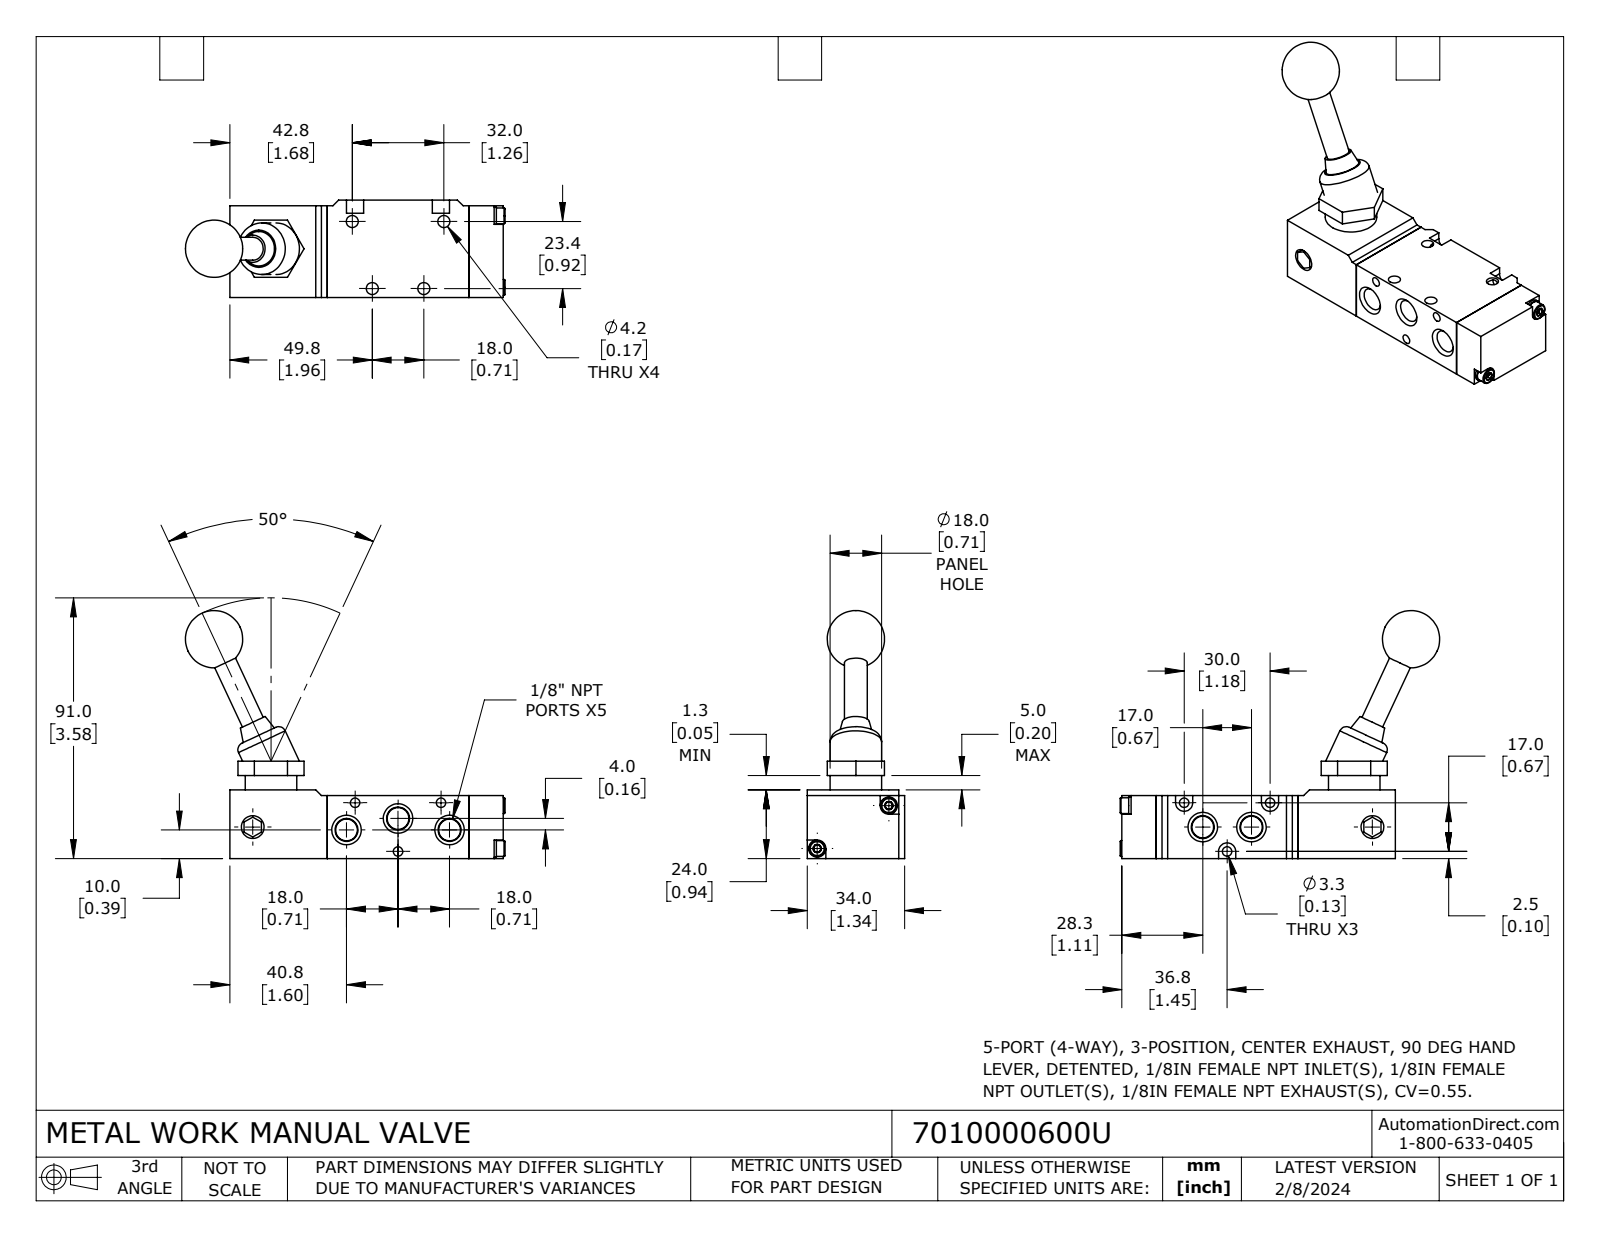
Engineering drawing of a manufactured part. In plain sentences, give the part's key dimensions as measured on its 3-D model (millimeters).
The part is named "7010000600U". Its 3-D file was written by "SolidWorks 2023 (CONFIG_CONTROL_DESIGN)". It is 8 solids with 208 faces: 105 planar, 49 cylindrical and 54 other. Overall it measures 111.6 by 86.6 by 34 millimeters. Its volume is 79 120 cubic millimeters and its surface area 22 500 square millimeters. Round holes: 4 of diameter 4.2, 3 of diameter 3.3, 2 of diameter 3, 1 of diameter 8. Round bosses or shafts: 2 of diameter 18, 2 of diameter 6, 2 of diameter 5.5, 1 of diameter 8. Partial cylindrical surfaces (rounded edges, fillets, slot ends): 3 of radius 3. The main face-to-face distances are 22, 34, 49.5, 2, 32, 12, 83.5, 24, 61.5, 95.5. The hole center spacings are 22.7, 24.4, 34.2, 18, 29.2, 30, 32, 36.8.
